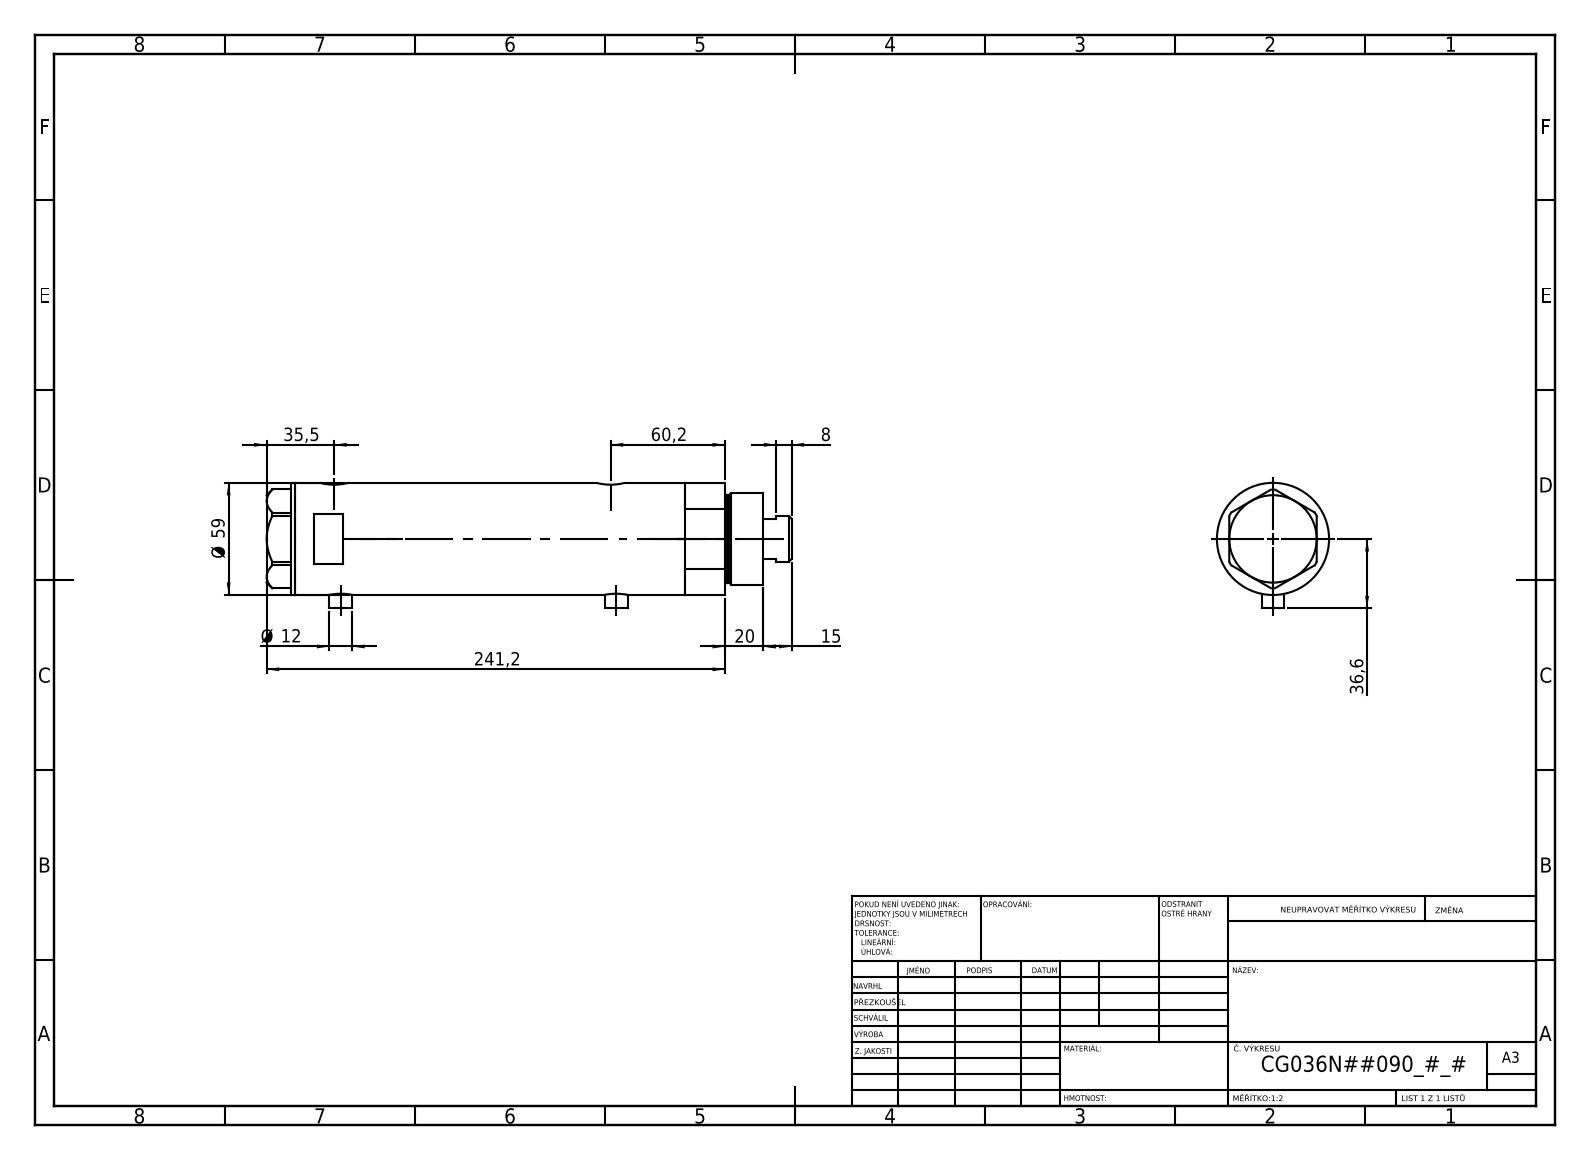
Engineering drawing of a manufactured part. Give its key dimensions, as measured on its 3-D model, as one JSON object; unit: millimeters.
{"part_name": "V270CG_MIDDLE; V270CG_BACK; V270CG_VC; V270CG_FRONT", "step_written_by": "SolidWorks 2019 (CONFIG_CONTROL_DESIGN)", "units": "millimeters", "bodies": {"solids": 4, "faces": 120, "planar": 51, "cylindrical": 49, "other": 20}, "overall_size": [276.2, 66.1, 59], "volume_mm3": 635072, "surface_area_mm2": 125343, "round_holes": [[9.73, 2], [12.5, 2], [15, 2], [8.5, 1], [25, 1], [26.5, 1], [36, 1], [40, 1], [52, 1]], "round_bosses_or_shafts": [[12, 2], [59, 1], [48, 1], [46, 1], [24, 1]], "face_to_face_distances": [167.2, 23.5, 143.7, 15, 38.5, 182.2, 2, 261.2, 246.2, 222.7], "hole_center_spacings": [2.9, 3.5, 142, 144.9, 145.5, 148.4]}
